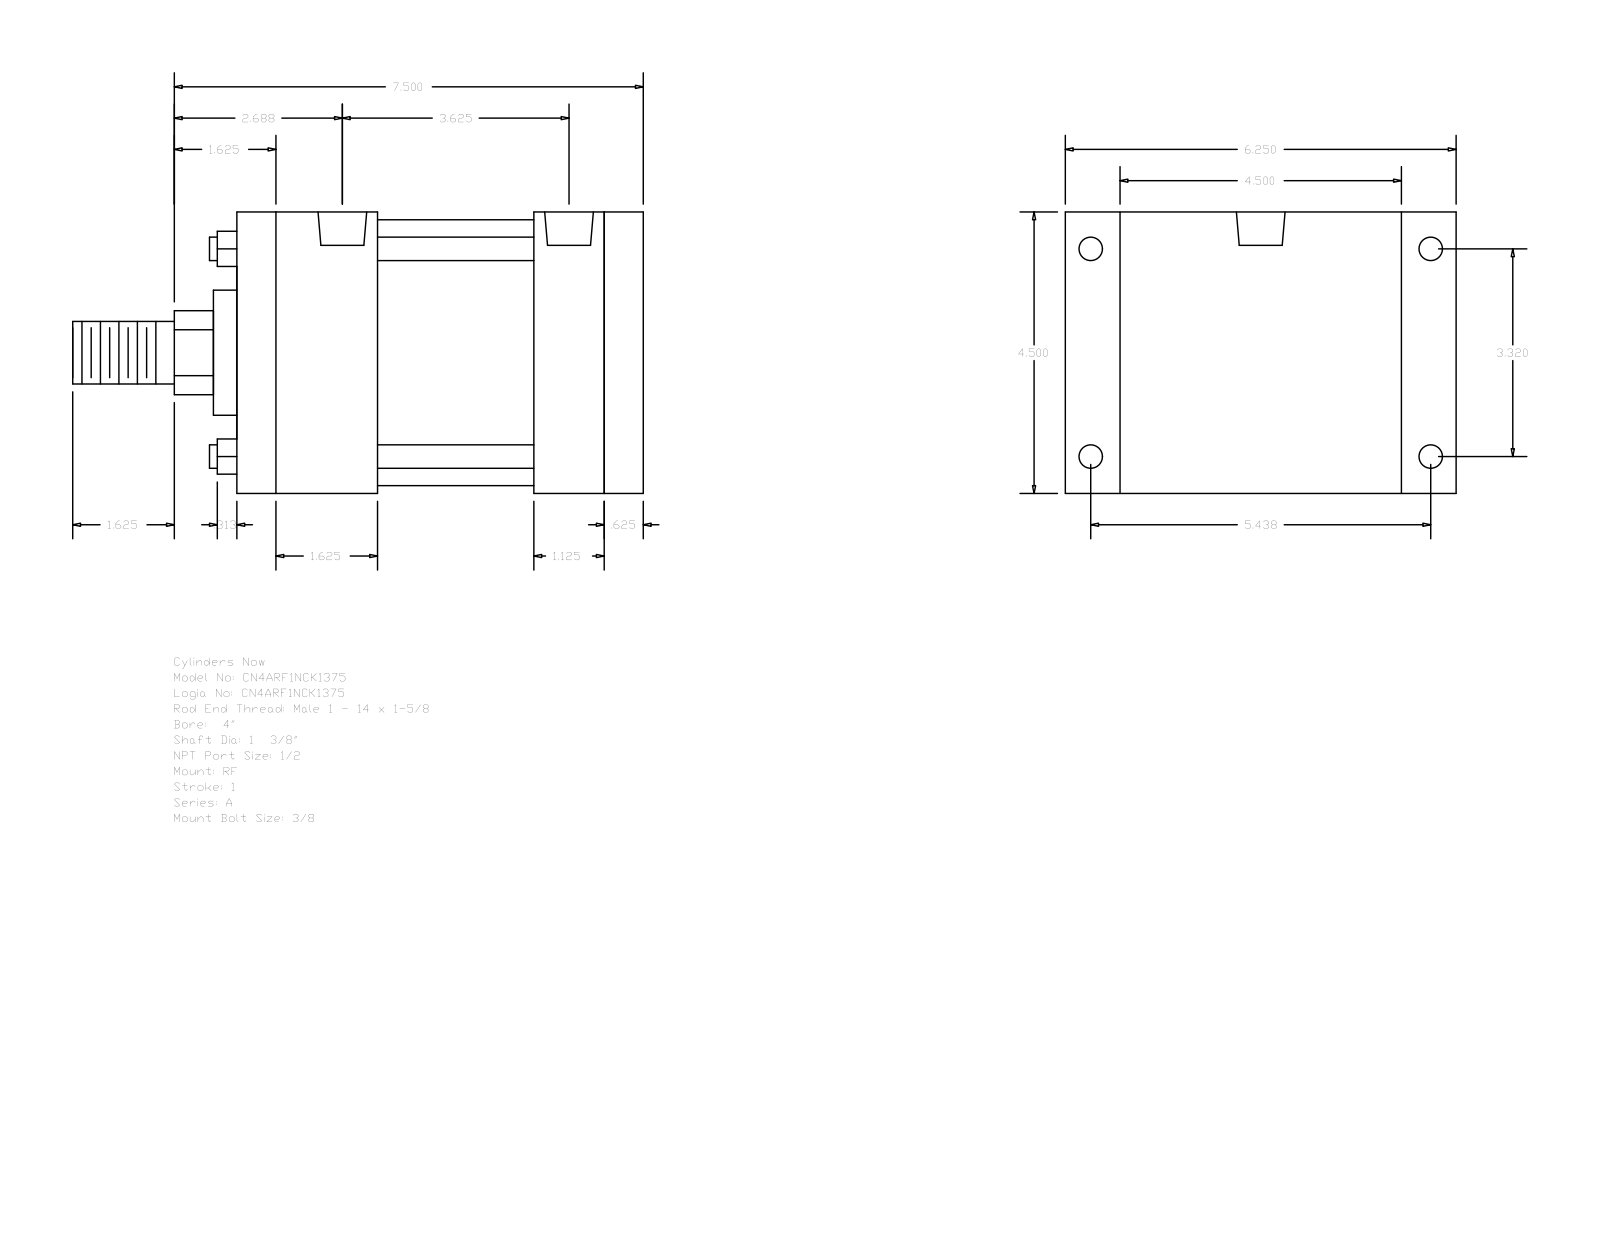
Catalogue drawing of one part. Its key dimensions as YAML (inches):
part_name: "A_RF__0400_1.375"
step_written_by: "GSSL Pune (CONFIG_CONTROL_DESIGN)"
units: inches
bodies: {solids: 0, faces: 92, planar: 64, cylindrical: 28, other: 0}
overall_size: [9.125, 6.25, 4.5]
round_holes:
  - {diameter: 0.344, count: 4}
  - {diameter: 0.375, count: 4}
  - {diameter: 0.778, count: 2}
round_bosses_or_shafts:
  - {diameter: 0.375, count: 4}
  - {diameter: 4.25, count: 1}
  - {diameter: 2, count: 1}
  - {diameter: 1.375, count: 1}
  - {diameter: 1, count: 1}
partial_cylinders:
  - {radius: 0.672, count: 1}
face_to_face_distances: [4.5, 6.5, 0.625, 5.875, 2.25, 0.875, 5.375, 4.75, 1.125, 1.75]
hole_center_spacings: [0.125, 3.32, 3.375, 3.5, 5.438, 6.371, 3.625]
